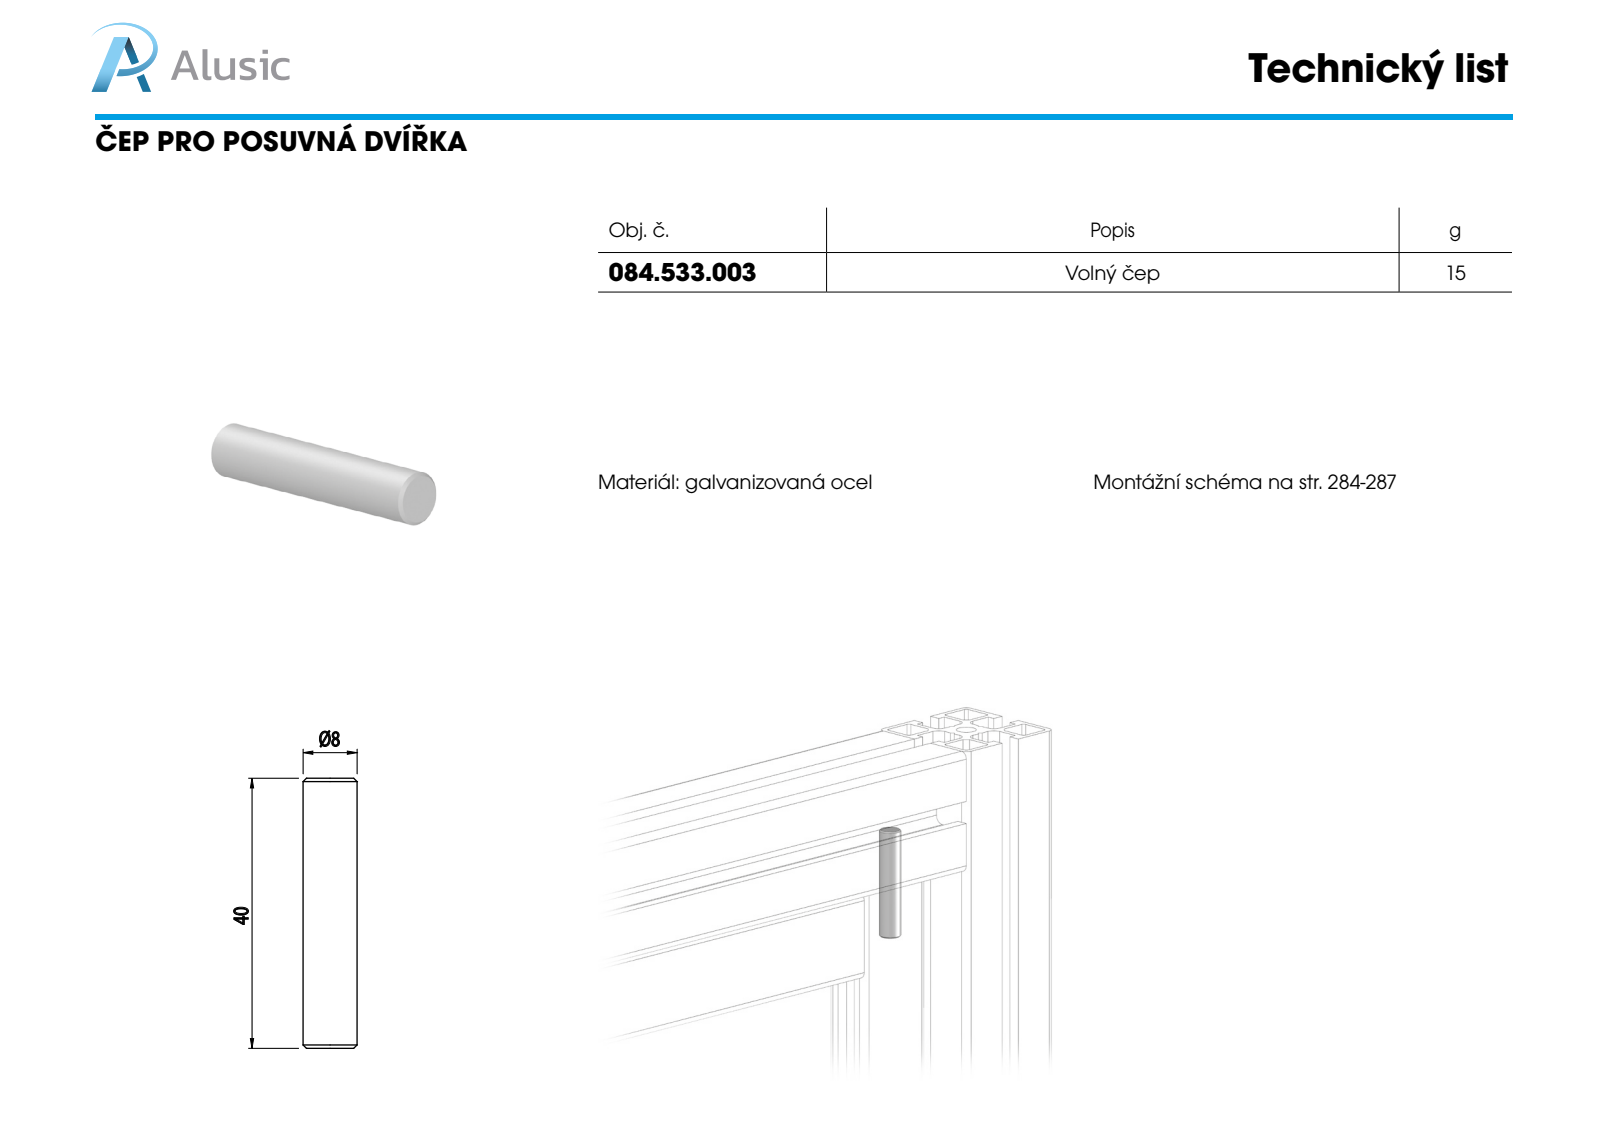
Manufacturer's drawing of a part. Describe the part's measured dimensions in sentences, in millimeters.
The part is named "084.533.003". Its 3-D file was written by "SolidWorks 2011 (CONFIG_CONTROL_DESIGN)". It is 1 solid with 8 faces: 2 planar, 2 cylindrical and 4 other. Overall it measures 40 by 8 by 8 millimeters. Its volume is 2 005 cubic millimeters and its surface area 1 090 square millimeters. Round bosses or shafts: 1 of diameter 8. The main face-to-face distances are 40.
